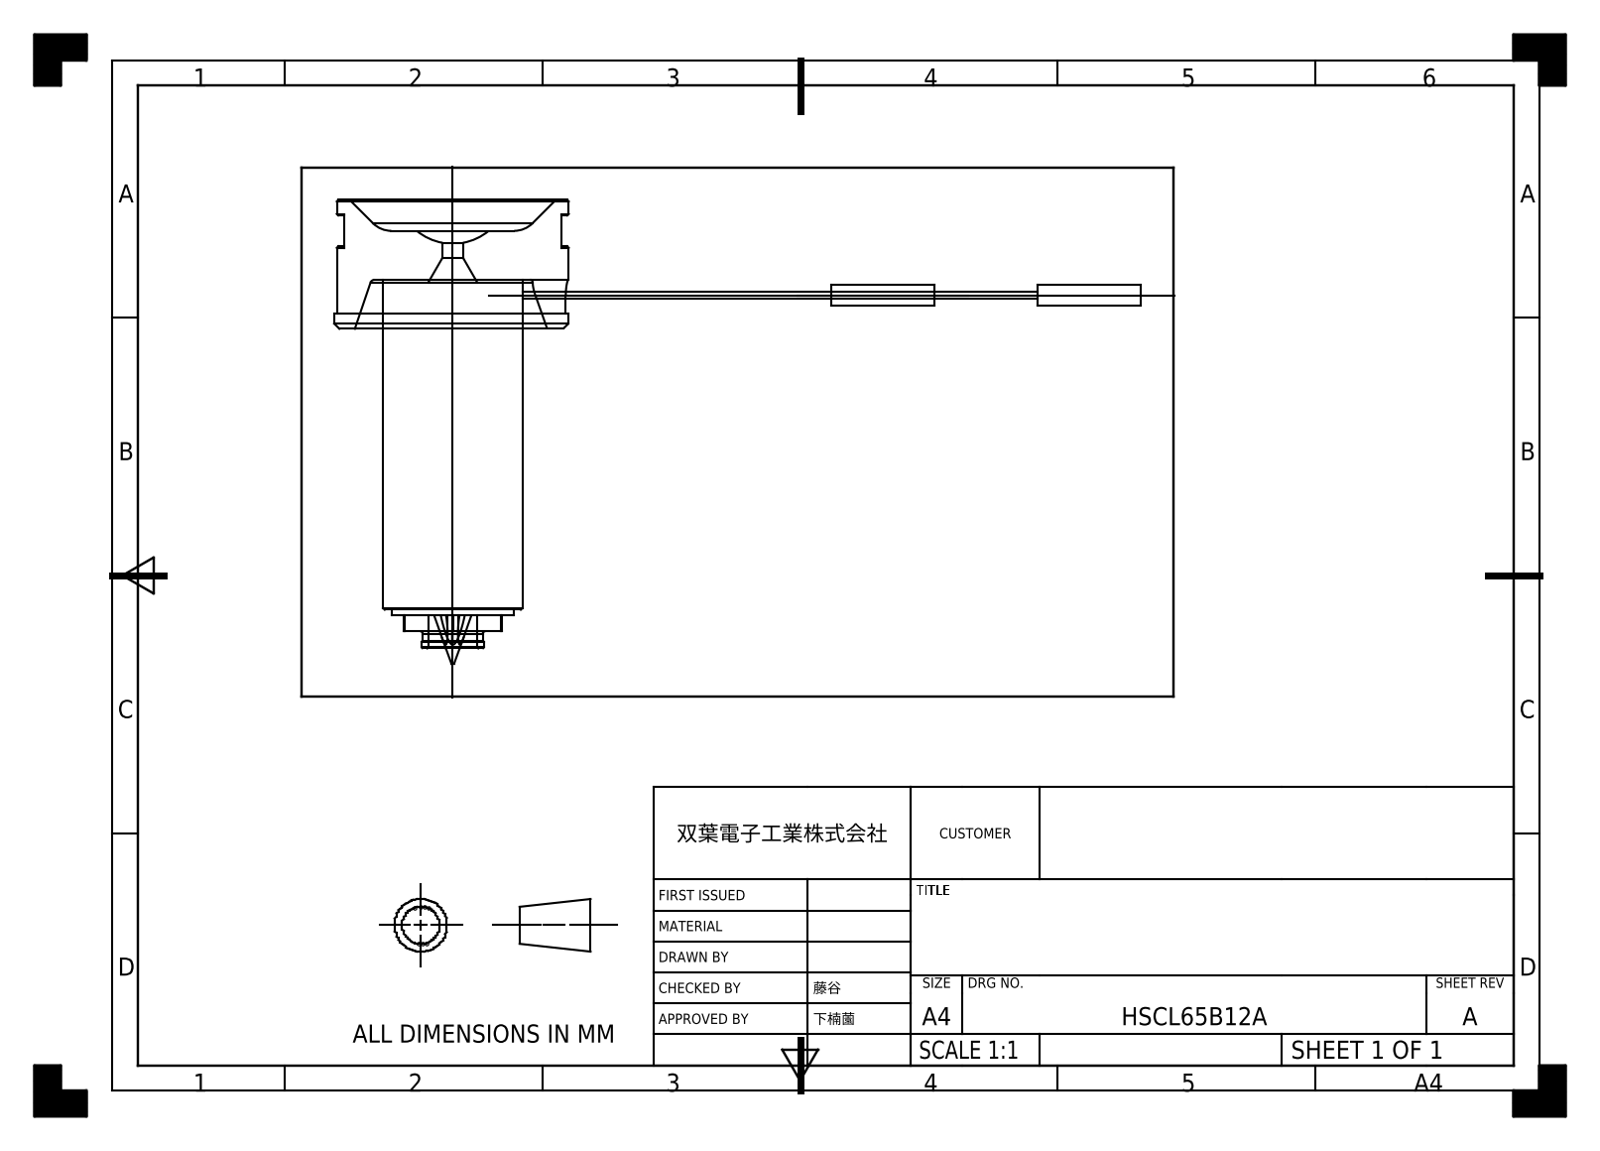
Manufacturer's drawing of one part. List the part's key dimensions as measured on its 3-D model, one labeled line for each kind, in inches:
Part name (STEP PRODUCT): HSCL65B12A
STEP written by: SIEMENS PLM Software NX 2023 (AUTOMOTIVE_DESIGN)
Units: inches
Bodies: 5 solids, 75 faces (34 planar, 23 cylindrical, 18 other)
Overall size (bounding box): 6.161 × 3.543 × 1.811
Volume: 3.849 in³ · Surface area: 23.57 in²
Round holes (diameter × count): ⌀0.157 ×1, ⌀0.374 ×1
Round bosses / shafts (diameter × count): ⌀0.157 ×2, ⌀0.047 ×2, ⌀1.811 ×1, ⌀1.772 ×1, ⌀1.063 ×1, ⌀0.937 ×1, ⌀0.472 ×1, ⌀0.457 ×1
Partial cylindrical surfaces — rounded edges, fillets, slot ends (radius × count): R0.11 ×3, R0.118 ×2, R0.429 ×1
Main face-to-face distances: 0.748, 0.236, 0.374, 0.984, 2.559, 3.295, 3.059, 2.311, 0.61, 2.685
